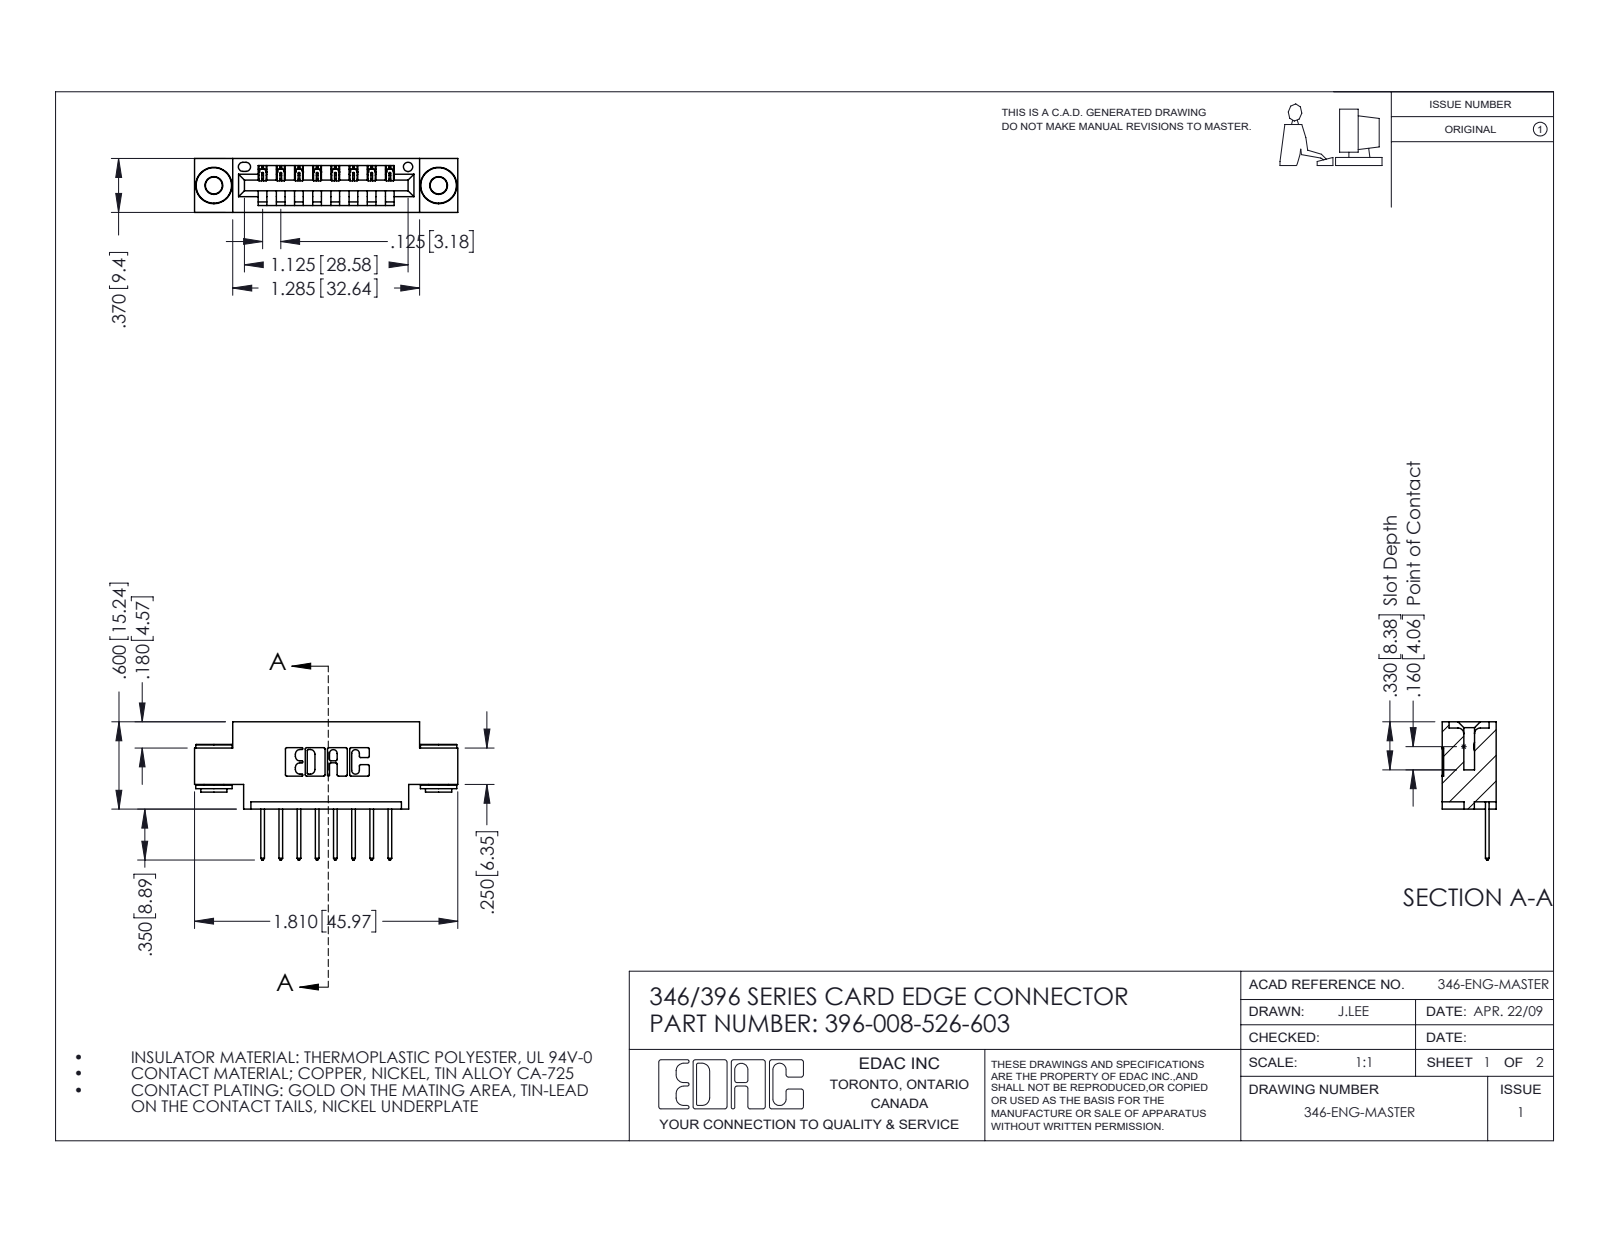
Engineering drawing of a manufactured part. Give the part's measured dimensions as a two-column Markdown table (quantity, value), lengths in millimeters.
| quantity | value |
| --- | --- |
| part name | 396-008-526-603; 346 Part_0.170 Offset - 0.156 Dia-TH; 345-292-001_345-293-126; 345-250-002_345-250-002-102 |
| STEP written by | SolidWorks 2016 (CONFIG_CONTROL_DESIGN) |
| units | millimeters |
| bodies | 11 solids, 628 faces (410 planar, 210 cylindrical, 8 other) |
| overall size | 46 × 24.1 × 9.4 |
| volume | 4 030 mm³ |
| surface area | 5 035 mm² |
| round holes (diameter × count) | 2.9 × 2, 4 × 2, 1.6 × 1 |
| round bosses / shafts (diameter × count) | 6.4 × 2, 4.6 × 2, 3.5 × 2 |
| partial cylindrical surfaces (radius × count) | 0.3 × 22, 0.2 × 16, 0.3 × 16, 0.2 × 6, 0.8 × 6, 0.7 × 3, 0.8 × 2, 1 × 2 |
| main face-to-face distances | 6.4, 9.4, 1.2, 8.2, 0.6, 1.8, 7.6, 3.8, 5.6, 2.5 |
| hole center spacings | 6.2, 34.1, 39.2 |
